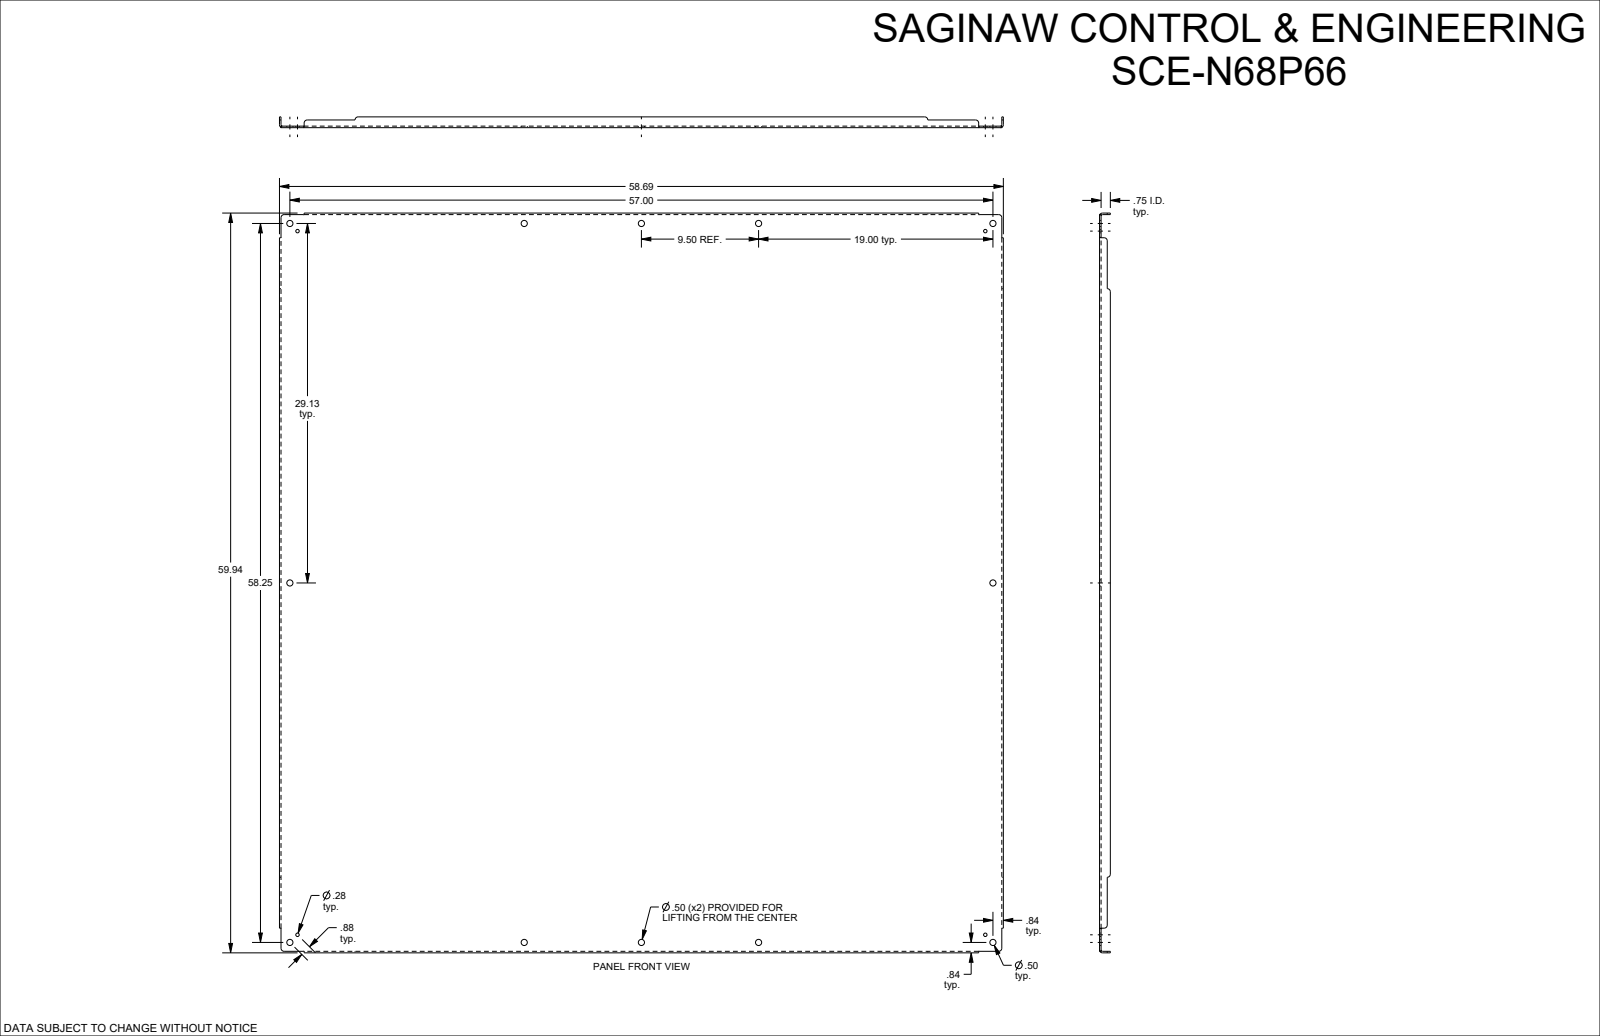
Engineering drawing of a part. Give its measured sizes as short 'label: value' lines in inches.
name: SCE-N68P66
written by: SolidWorks 2023 (AUTOMOTIVE_DESIGN)
unit: in
bodies: 1 solid, 130 faces (46 planar, 60 cylindrical, 24 other)
size: 59.938 × 58.688 × 0.875
volume: 456.7 in³; area: 7 341 in²
holes: 12× ⌀0.5, 4× ⌀0.281
rounds: 12× R0.25, 4× R0.112, 4× R0.237
face distances: 0.125, 58.563, 0.125, 59.813, 58.438, 58.687, 59.687, 59.938, 0.75, 0.875
hole spacings: 19, 61.27, 58.25, 0.875, 9.5, 18.391, 27.888, 28.5
